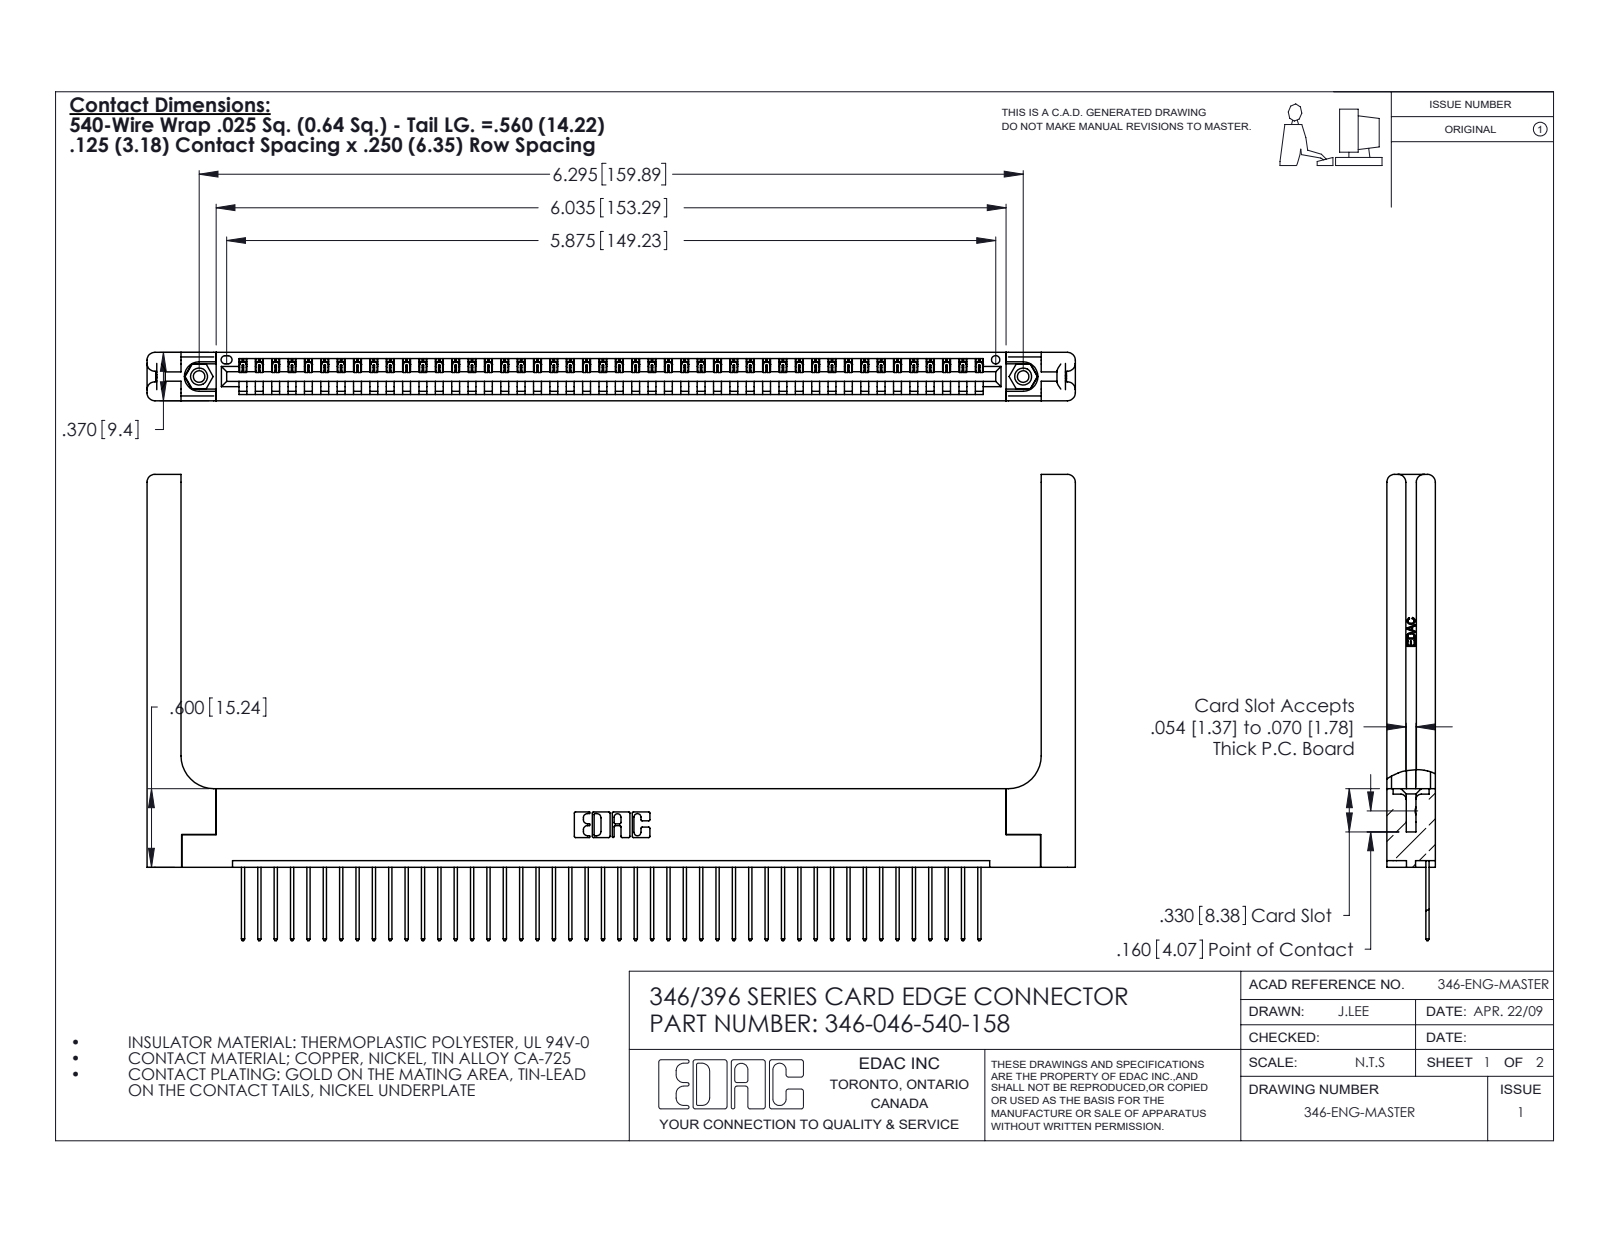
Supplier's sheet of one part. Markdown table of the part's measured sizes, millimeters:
| quantity | value |
| --- | --- |
| part name | 346-220-058_345-220-058; 345-292-001_345-293-140; 346-046-540-158; 345-250-001_345-250-001-102 (+1 more) |
| STEP written by | SolidWorks 2020 (CONFIG_CONTROL_DESIGN) |
| units | millimeters |
| bodies | 51 solids, 3060 faces (2078 planar, 922 cylindrical, 60 other) |
| overall size | 180.1 × 90.4 × 9.4 |
| volume | 24 830 mm³ |
| surface area | 27 340 mm² |
| round holes (diameter × count) | 2.3 × 2, 3.2 × 2, 4 × 2, 1.6 × 1 |
| round bosses / shafts (diameter × count) | 3.9 × 2 |
| partial cylindrical surfaces (radius × count) | 0.2 × 92, 0.3 × 92, 0.3 × 22, 1.5 × 16, 0.2 × 6, 0.8 × 6, 0.7 × 3, 0.8 × 2 |
| main face-to-face distances | 9.4, 1.2, 8.2, 1.8, 3.8, 3.8, 6.4, 7.6, 0.6, 5.6 |
| hole center spacings | 6.2, 154.6, 159.9 |
